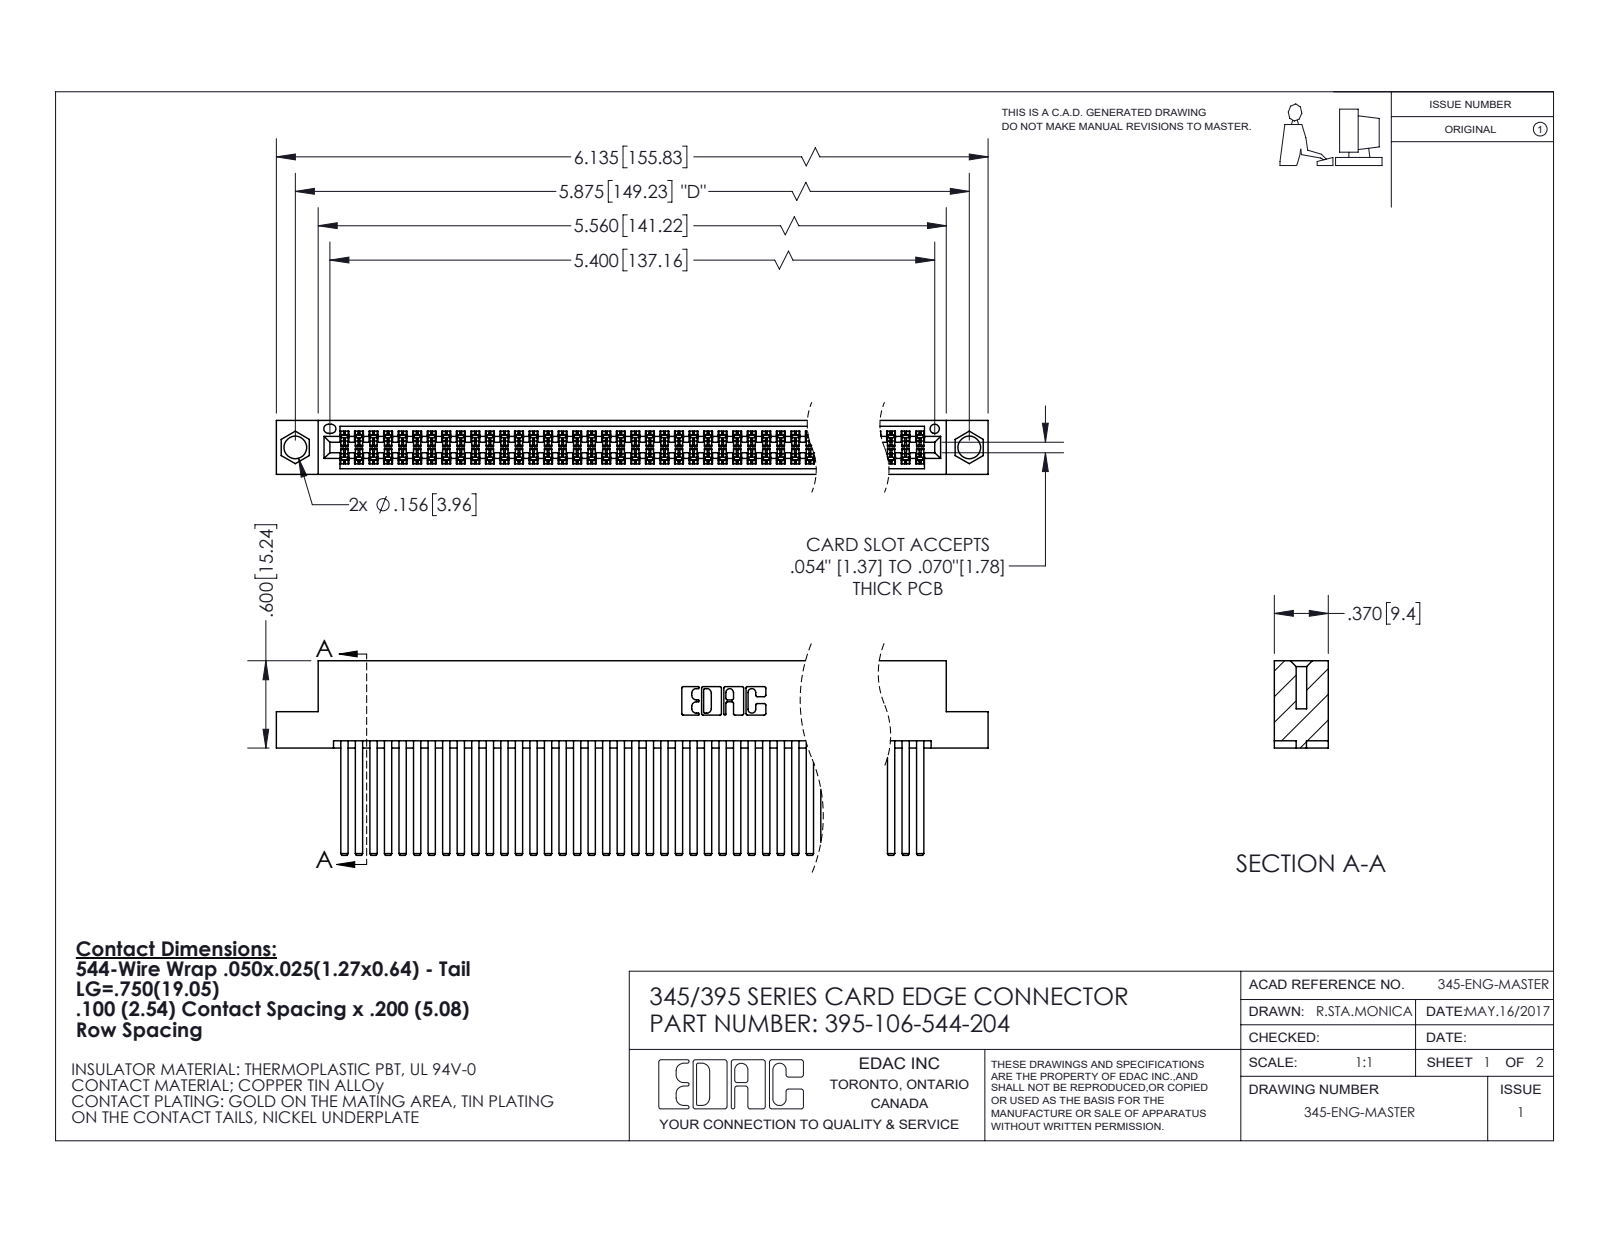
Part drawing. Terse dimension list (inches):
name: 345 Part_Flush Mounting Lugs - 0.156 Dia-TI; 345-292-001_345-293-144; 395-106-544-204
written by: SolidWorks 2020 (CONFIG_CONTROL_DESIGN)
unit: in
bodies: 107 solids, 4804 faces (3168 planar, 1636 cylindrical, 0 other)
size: 6.135 × 1.337 × 0.37
volume: 1.014 in³; area: 44.93 in²
holes: 2× ⌀0.156, 1× ⌀0.064
rounds: 159× R0.006, 22× R0.01, 6× R0.007, 6× R0.031, 3× R0.026, 2× R0.014, 2× R0.019, 2× R0.022
face distances: 0.2, 0.025, 0.298, 0.072, 0.098, 0.272, 0.225, 0.175, 0.37, 0.05
hole spacings: 0.27, 5.639, 5.875
